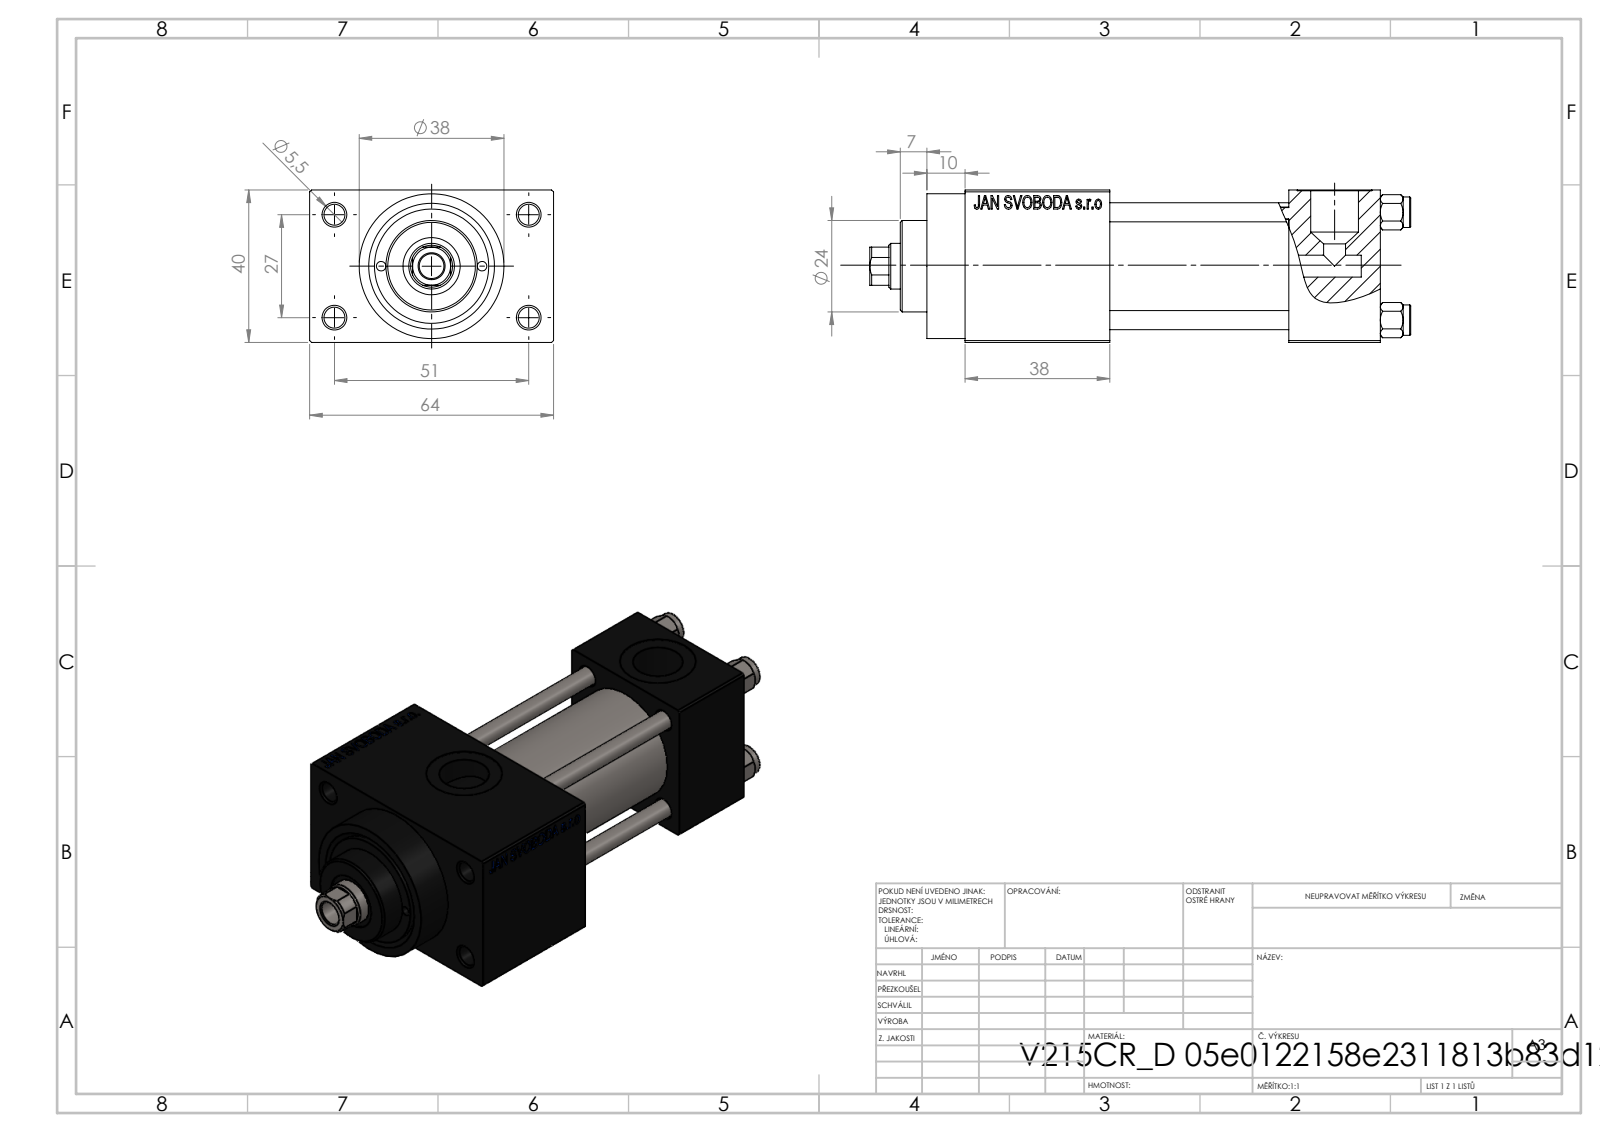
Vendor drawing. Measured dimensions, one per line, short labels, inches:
name: NUT_M5_D; V215_VC_A; V215CR_D_Body; V215CR_D_TYCINKA (+1 more)
written by: SolidWorks 2019 (CONFIG_CONTROL_DESIGN)
unit: in
bodies: 11 solids, 1111 faces (498 planar, 93 cylindrical, 520 other)
size: 5.591 × 2.52 × 1.575
volume: 10.68 in³; area: 95.58 in²
holes: 4× ⌀0.197, 4× ⌀0.217, 3× ⌀0.787, 2× ⌀0.098, 2× ⌀0.276, 2× ⌀0.518, 1× ⌀0.256, 1× ⌀0.472, 1× ⌀0.591, 1× ⌀0.984, 1× ⌀1.181
bosses: 4× ⌀0.315, 1× ⌀1.496, 1× ⌀1.22, 1× ⌀0.945
rounds: 1× R0.217
face distances: 1.575, 0.472, 2.047, 1.85, 0.945, 2.795, 2.52, 1.496, 4.291, 3.346
hole spacings: 0.448, 0.558, 0.718, 0.788, 1.114, 1.136, 1.177, 1.214
